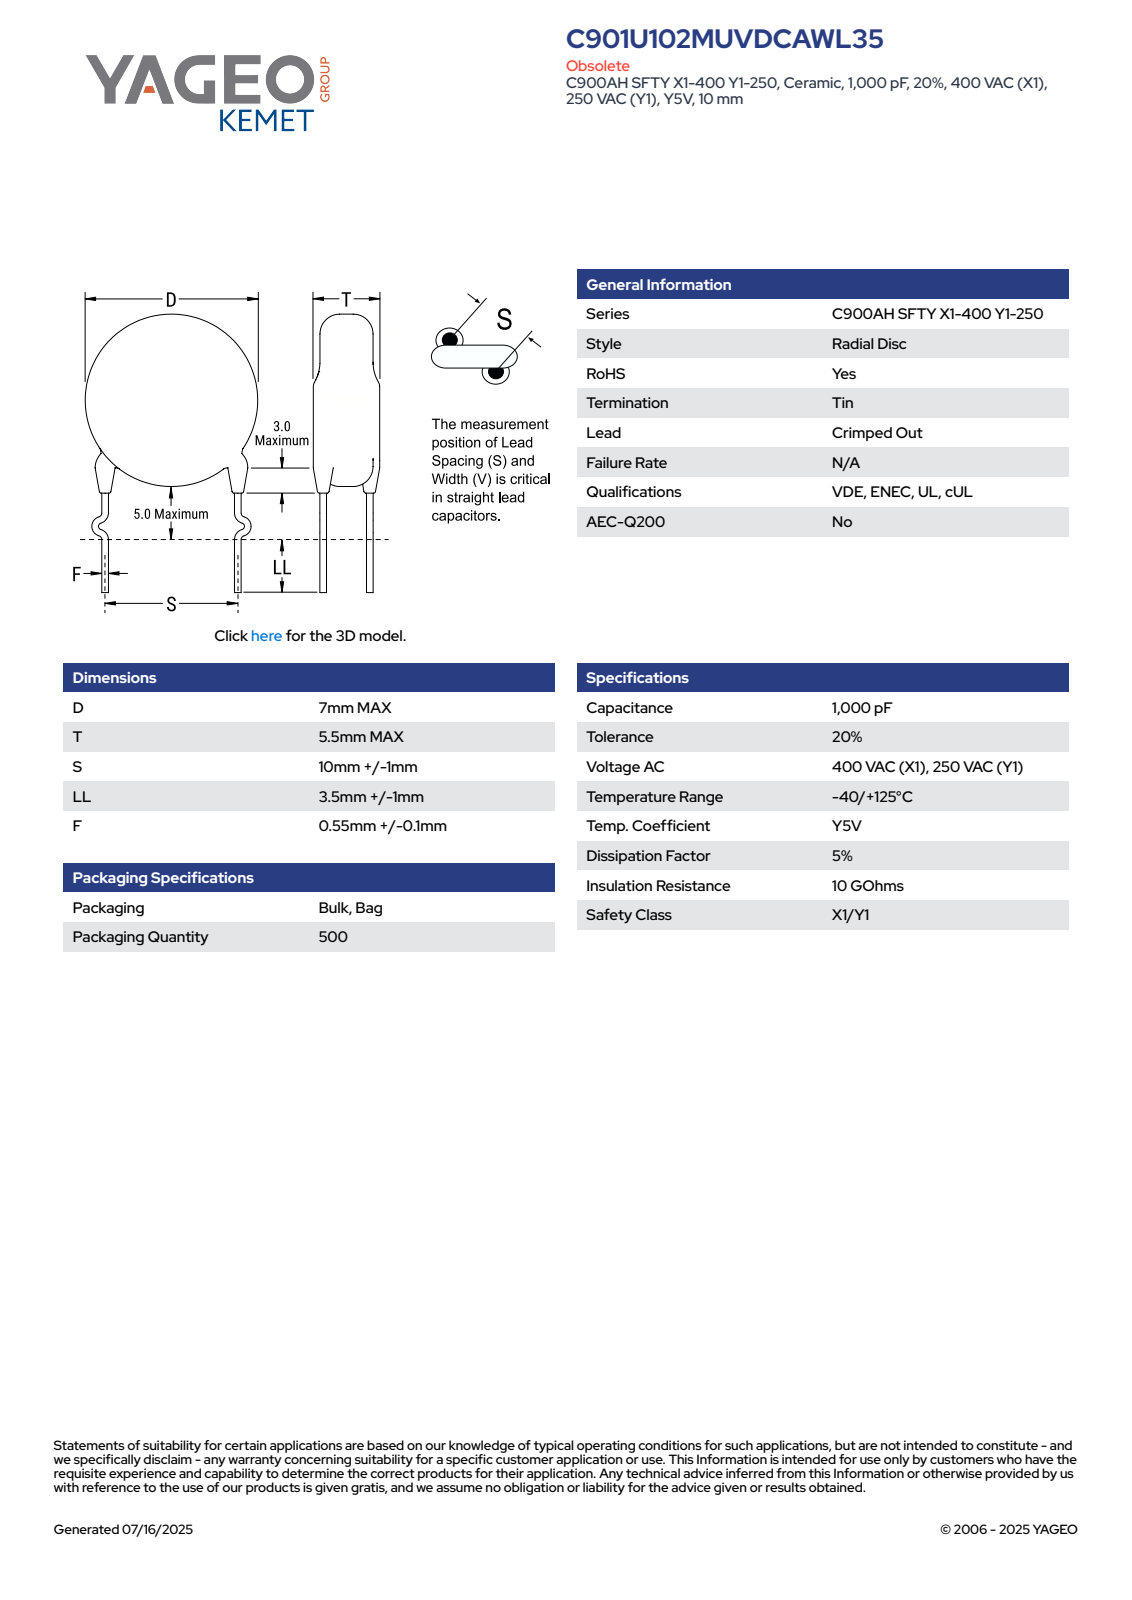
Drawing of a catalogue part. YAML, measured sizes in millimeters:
part_name: "CCD_KCOC900_D7T5.5S10LL4.5F0.55"
step_written_by: "SolidWorks 2014 (AUTOMOTIVE_DESIGN)"
units: millimeters
bodies: {solids: 4, faces: 93, planar: 63, cylindrical: 10, other: 20}
overall_size: [16.5, 13.59, 7.28]
volume: 217
surface_area: 253
round_bosses_or_shafts:
  - {diameter: 1.2, count: 4}
  - {diameter: 7, count: 1}
face_to_face_distances: [5.5, 0.73, 3.87, 3.14, 0.59, 0.32, 2.97, 1.5, 2.16, 2.24]
